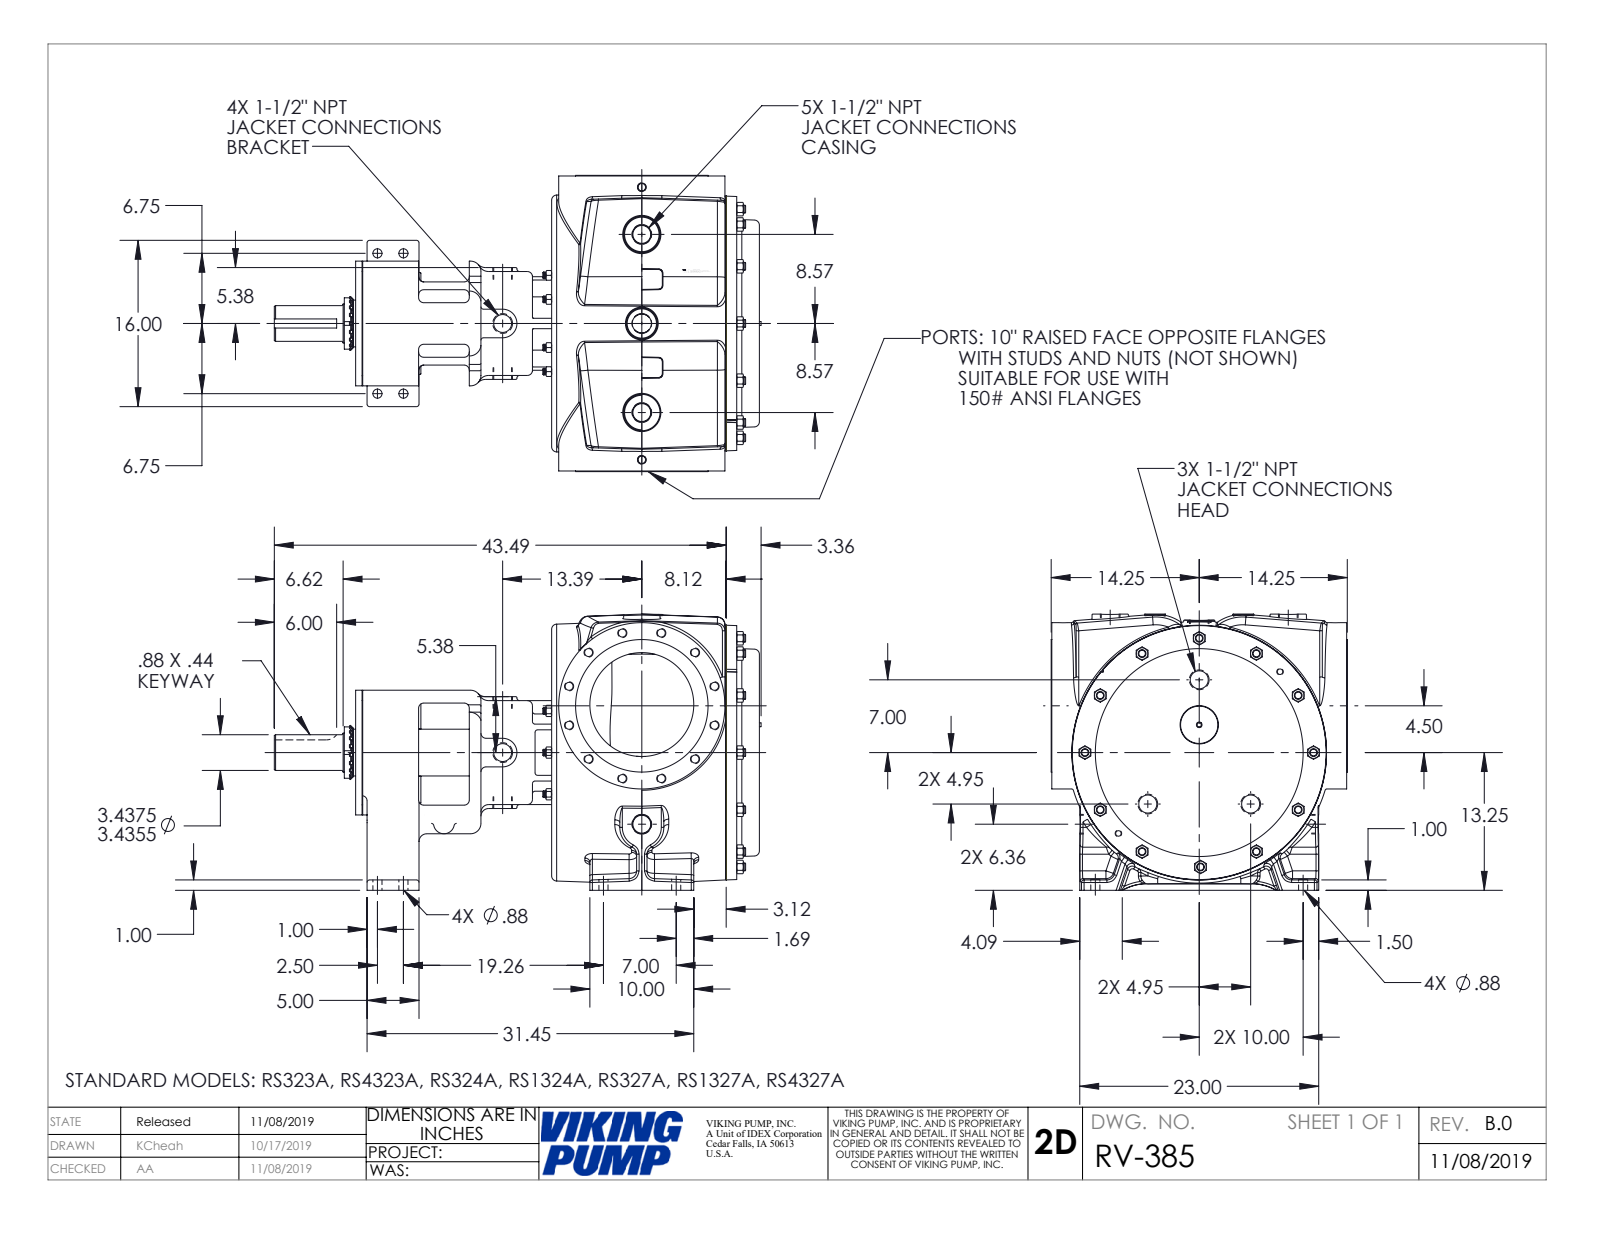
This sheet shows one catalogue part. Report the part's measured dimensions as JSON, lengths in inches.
{"part_name": "RV-385", "step_written_by": "SolidWorks 2024 (AUTOMOTIVE_DESIGN)", "units": "inches", "bodies": {"solids": 1, "faces": 5374, "planar": 1809, "cylindrical": 957, "other": 2608}, "overall_size": [57.473, 34.703, 26.57], "volume_in3": 13618, "surface_area_in2": 6206, "round_holes": [[0.266, 26], [0.875, 16], [1.63, 12], [0.25, 8], [0.688, 6], [0.81, 6], [0.875, 5], [1.384, 4], [0.312, 2], [0.531, 2], [0.69, 2], [1.34, 2]], "round_bosses_or_shafts": [[0.866, 12], [0.742, 12], [0.625, 6], [0.617, 6], [1.613, 5], [0.875, 4], [7.38, 2], [0.375, 2]], "partial_cylinders_radius": [[0.25, 105], [0.12, 68], [0.03, 26], [1.12, 14], [0.5, 10], [0.06, 8], [1, 6], [0.37, 4]], "face_to_face_distances": [18.005, 0.44, 27.94, 0.06, 0.5, 28, 28.44, 27.5, 1, 28.38], "hole_center_spacings": [7.125, 11, 3.688, 9.567, 10.076, 12.341, 13.765, 5.694]}
